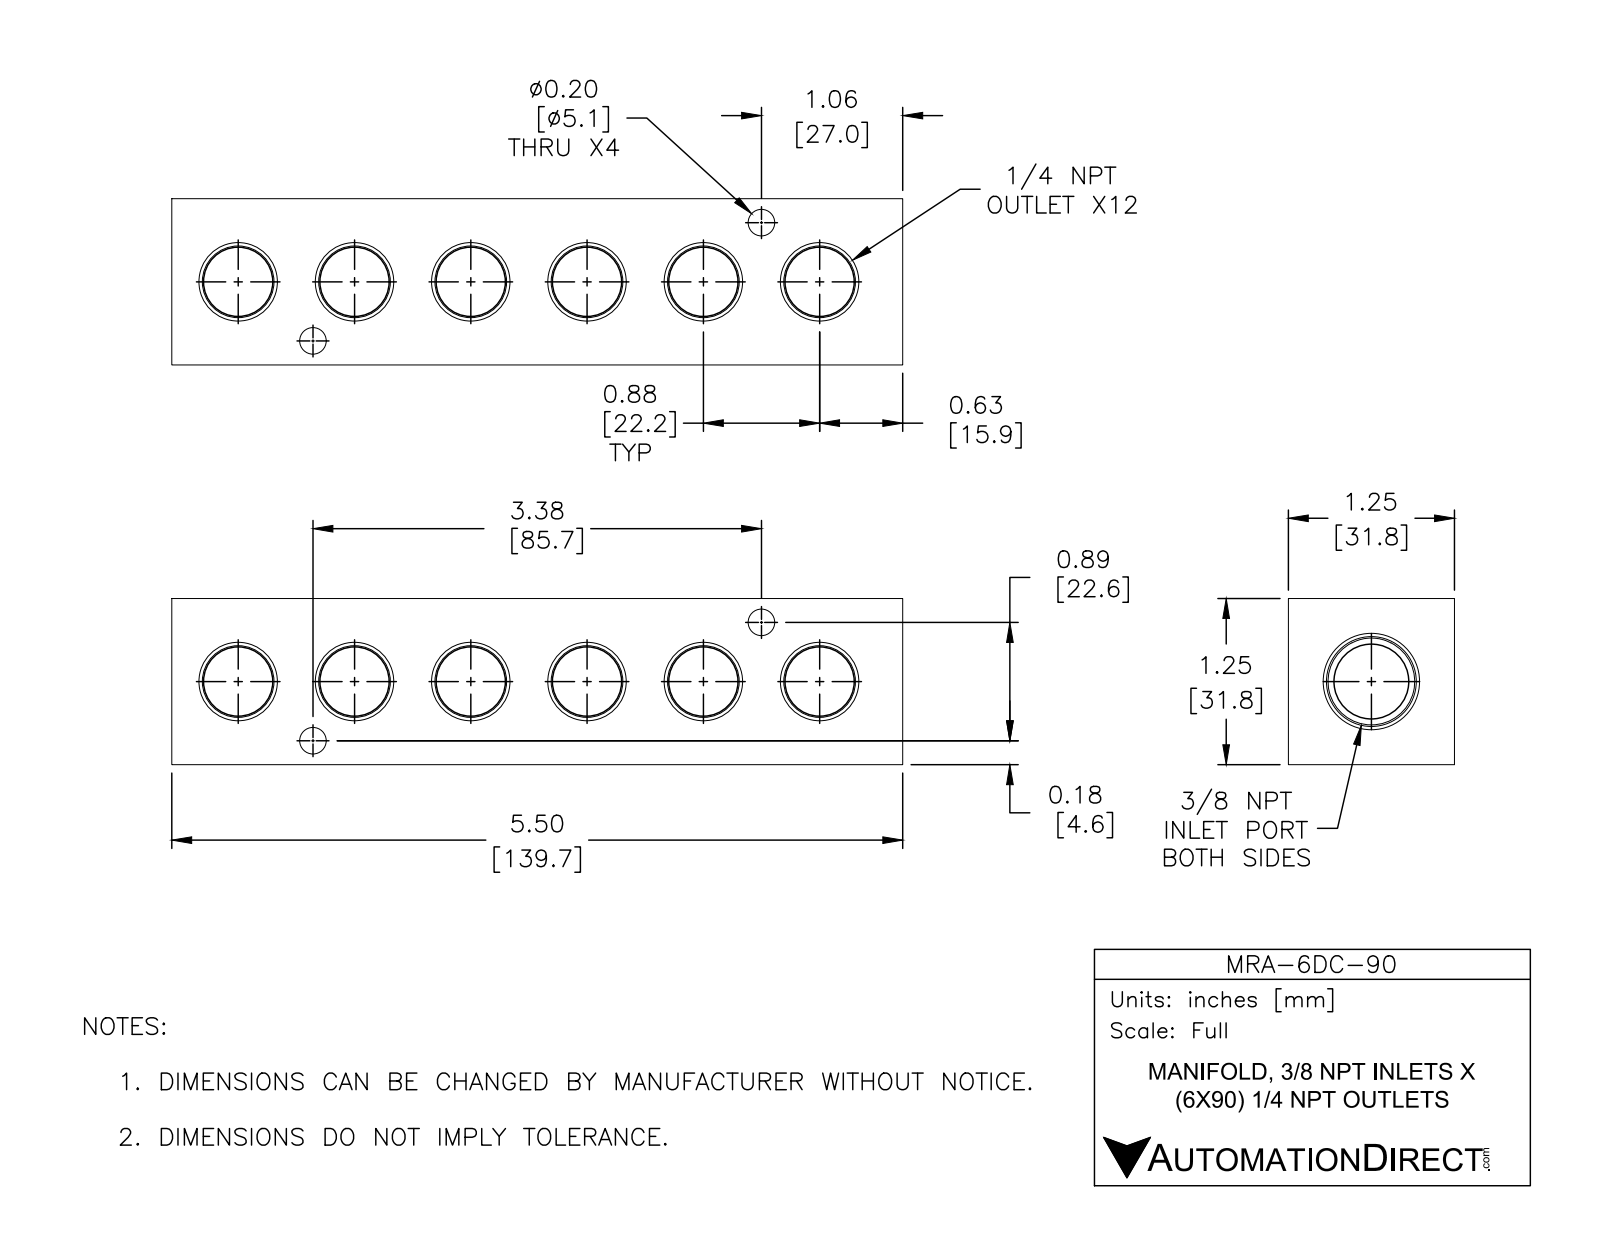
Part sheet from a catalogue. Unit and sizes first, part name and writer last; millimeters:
Units: millimetres
Overall size (bounding box): 142.9 × 31.8 × 31.8
Round holes (diameter × count): ⌀5.1 ×4, ⌀14.3 ×1
Partial cylindrical surfaces — rounded edges, fillets, slot ends (radius × count): R5.6 ×12
Main face-to-face distances: 31.8, 142.9, 21.8, 9.9, 10.4, 132.5, 122
Hole centre spacings: 91.7
Volume: 101 300 mm³ · Surface area: 29 720 mm²
Bodies: 1 solid, 134 faces (34 planar, 44 cylindrical, 56 other)
Part name (STEP PRODUCT): MRA-6DC-90
STEP written by: SolidWorks 2015 (CONFIG_CONTROL_DESIGN)
